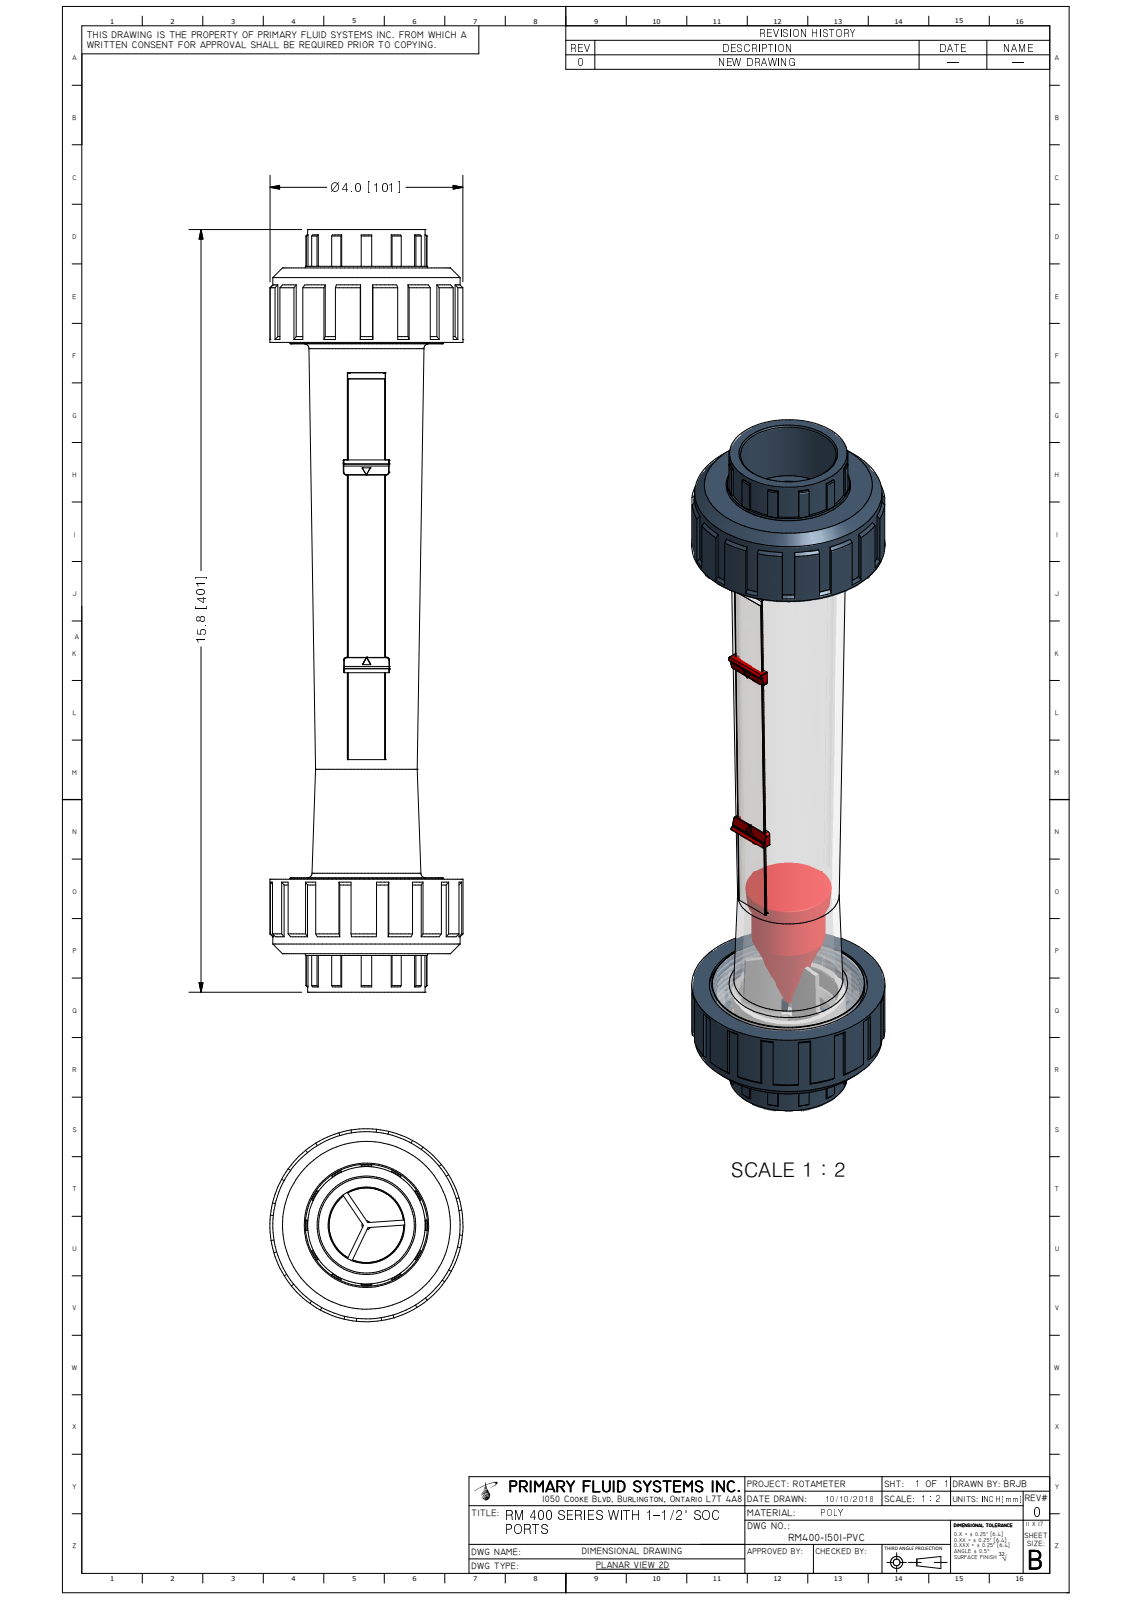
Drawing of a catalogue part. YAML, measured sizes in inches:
part_name: "RM400-150I-PVC_R0"
step_written_by: "Autodesk Inventor 2009 (AUTOMOTIVE_DESIGN)"
units: inches
bodies: {solids: 1, faces: 669, planar: 261, cylindrical: 132, other: 276}
overall_size: [15.77, 3.99, 3.99]
volume: 77.65
surface_area: 276.7
round_holes:
  - {diameter: 1.977, count: 1}
  - {diameter: 2.57, count: 1}
  - {diameter: 3.147, count: 1}
  - {diameter: 3.265, count: 1}
  - {diameter: 3.265, count: 1}
round_bosses_or_shafts:
  - {diameter: 3.99, count: 1}
  - {diameter: 3.87, count: 1}
  - {diameter: 3.158, count: 1}
  - {diameter: 3, count: 1}
  - {diameter: 2.523, count: 1}
  - {diameter: 2.428, count: 1}
partial_cylinders:
  - {radius: 0.008, count: 18}
  - {radius: 0.01, count: 16}
  - {radius: 0.004, count: 8}
  - {radius: 0.006, count: 8}
  - {radius: 0.06, count: 4}
  - {radius: 0.008, count: 2}
  - {radius: 0.04, count: 2}
  - {radius: 0.75, count: 2}
face_to_face_distances: [1.54, 12.64, 0.463, 13.717, 1.077, 12.177, 1.57, 12.61, 1.107, 12.147]
